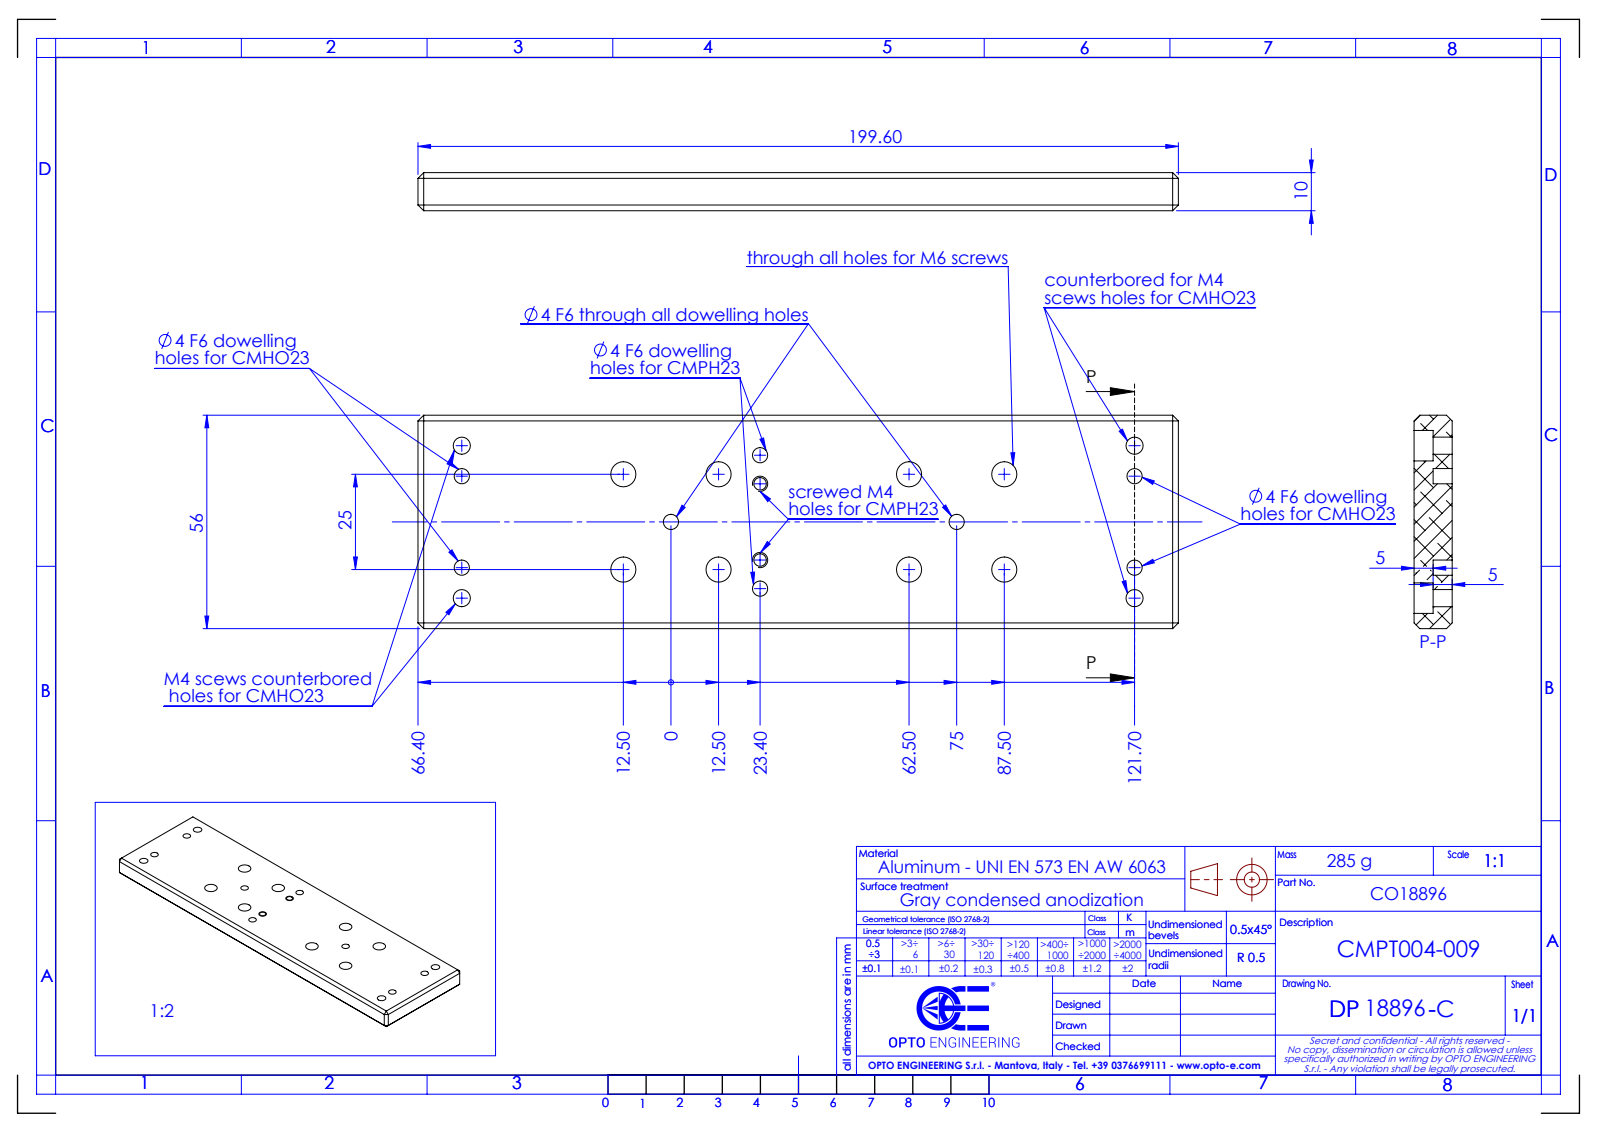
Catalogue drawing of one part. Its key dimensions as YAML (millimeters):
part_name: "DP18896"
step_written_by: "SolidWorks 2021 (CONFIG_CONTROL_DESIGN)"
units: millimeters
bodies: {solids: 1, faces: 88, planar: 36, cylindrical: 52, other: 0}
overall_size: [199.6, 56, 10]
volume: 105739
surface_area: 29048
round_holes:
  - {diameter: 4, count: 8}
  - {diameter: 6.6, count: 8}
  - {diameter: 4.5, count: 4}
  - {diameter: 8, count: 4}
  - {diameter: 3.3, count: 2}
face_to_face_distances: [10, 56, 44.55, 5, 199.6, 146.07, 178.59, 149.79]
hole_center_spacings: [25, 17.68, 75, 8, 32, 35.36, 63.74, 79.06]
